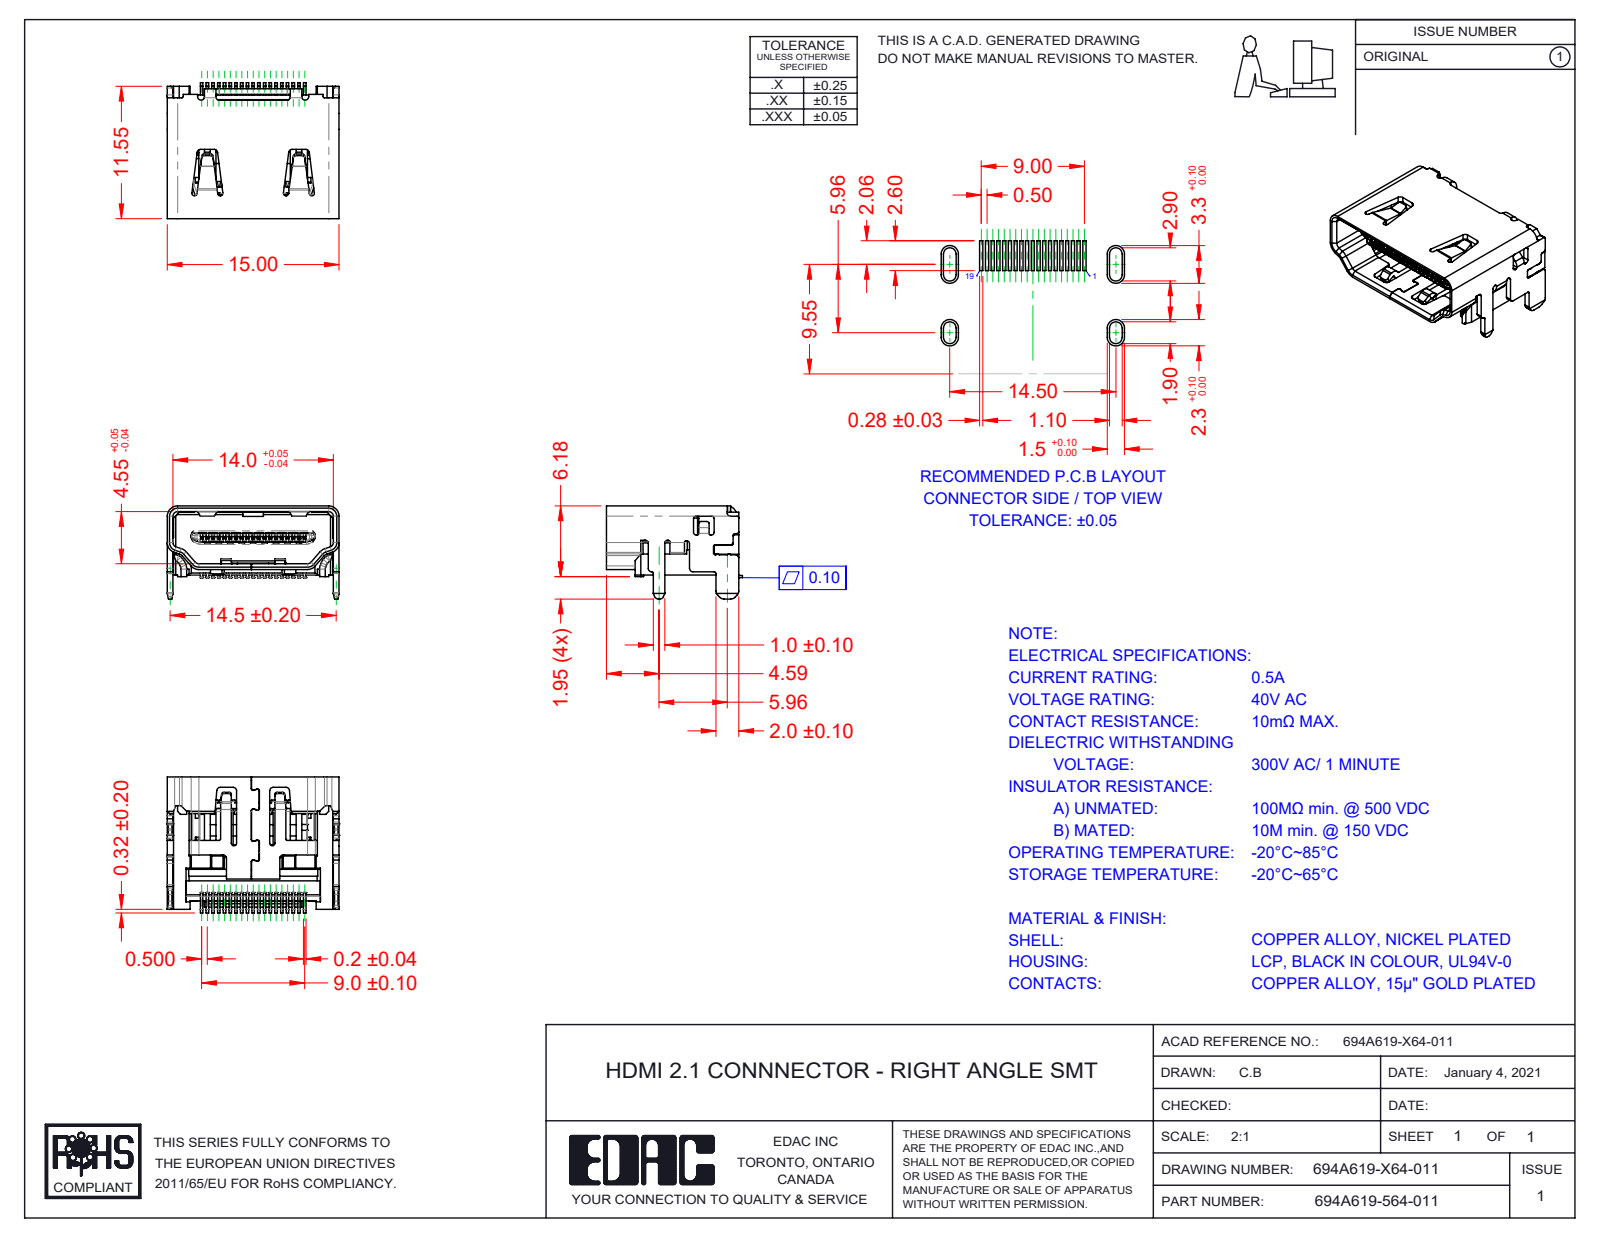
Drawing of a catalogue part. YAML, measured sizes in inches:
part_name: "Insulator 694A619-X64-011; Shell 694A619-X64-011; 694A619-164-011"
step_written_by: "SolidWorks 2020 (AUTOMOTIVE_DESIGN)"
units: inches
bodies: {solids: 2, faces: 2032, planar: 1473, cylindrical: 480, other: 79}
overall_size: [0.591, 0.467, 0.32]
volume: 0.028
surface_area: 2.465
partial_cylinders:
  - {radius: 0.008, count: 36}
  - {radius: 0.005, count: 30}
  - {radius: 0.012, count: 21}
  - {radius: 0.006, count: 20}
  - {radius: 0.02, count: 10}
  - {radius: 0.007, count: 8}
  - {radius: 0.016, count: 8}
  - {radius: 0.004, count: 6}
face_to_face_distances: [0.02, 0.022, 0.199, 0.179, 0.571, 0.11, 0.069, 0.219, 0.028, 0.089]
